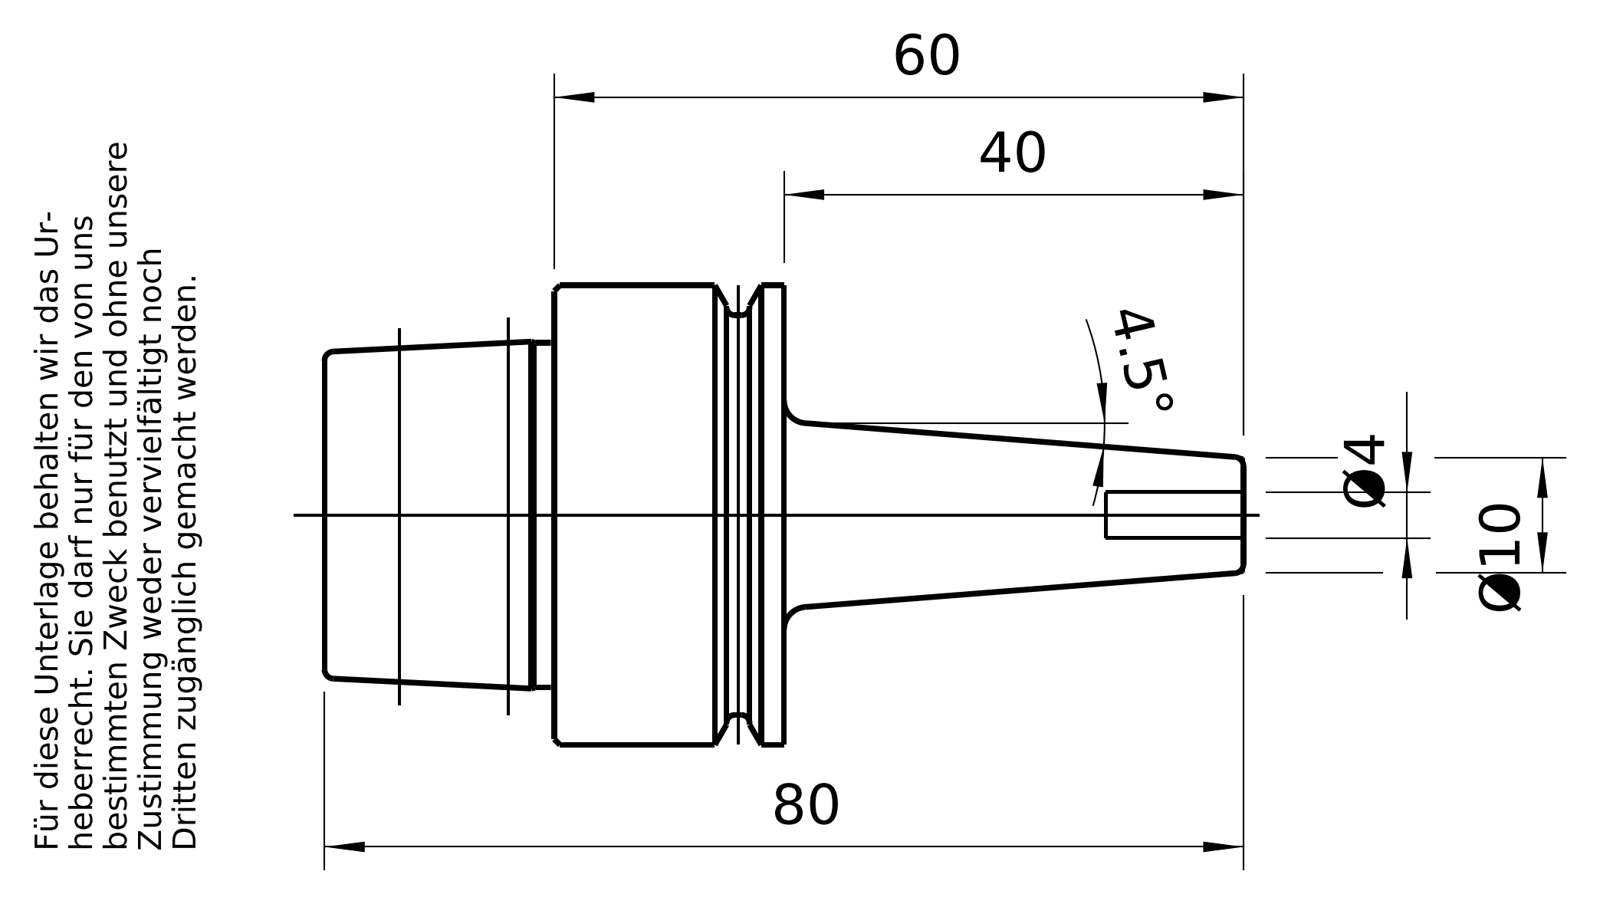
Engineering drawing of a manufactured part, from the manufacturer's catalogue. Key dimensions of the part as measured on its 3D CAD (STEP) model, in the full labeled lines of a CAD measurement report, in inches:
Part name (STEP PRODUCT): E40-140-04
STEP written by: PRO/ENGINEER BY PARAMETRIC TECHNOLOGY CORPORATION, 2010430 (CONFIG_CONTROL_DESIGN)
Units: inches
Bodies: 1 solid, 77 faces (9 planar, 22 cylindrical, 46 other)
Overall size (bounding box): 3.146 × 1.575 × 1.575
Volume: 1.886 in³ · Surface area: 17.38 in²
Round holes (diameter × count): ⌀0.157 ×1, ⌀0.402 ×1, ⌀0.481 ×1, ⌀0.492 ×1, ⌀0.828 ×1, ⌀1.007 ×1
Round bosses / shafts (diameter × count): ⌀1.575 ×1, ⌀1.368 ×1, ⌀1.174 ×1
Main face-to-face distances: 0.785, 0.472, 0.783, 1.569, 1.096, 0.313, 1.411, 0.628, 0.315, 0.157
